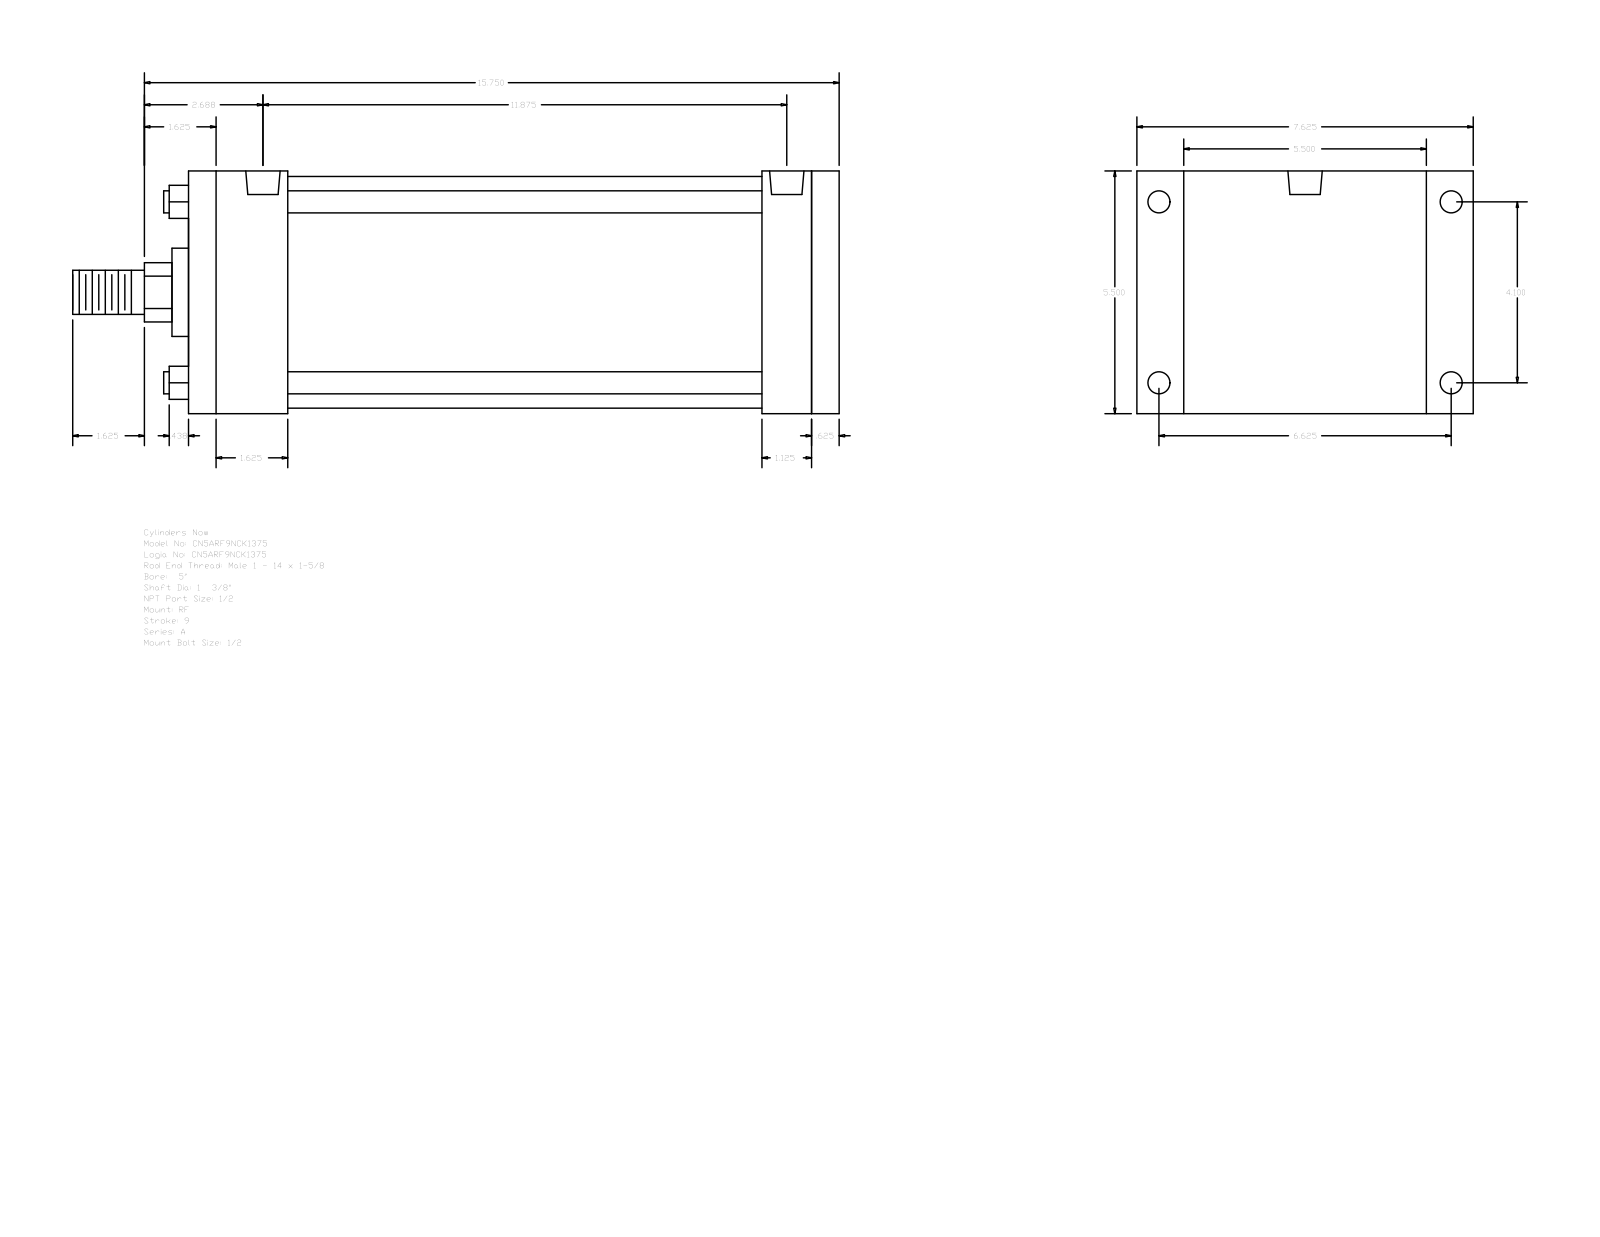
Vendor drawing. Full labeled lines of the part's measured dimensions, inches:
Part name (STEP PRODUCT): A_RF__0500_1.375
STEP written by: GSSL Pune (CONFIG_CONTROL_DESIGN)
Units: inches
Bodies: 0 solids, 92 faces (64 planar, 28 cylindrical, 0 other)
Overall size (bounding box): 17.375 × 7.625 × 5.5
Round holes (diameter × count): ⌀0.344 ×4, ⌀0.5 ×4, ⌀0.778 ×2
Round bosses / shafts (diameter × count): ⌀0.5 ×4, ⌀5.25 ×1, ⌀2 ×1, ⌀1.375 ×1, ⌀1 ×1
Partial cylindrical surfaces — rounded edges, fillets, slot ends (radius × count): R0.672 ×1
Main face-to-face distances: 5.5, 14.75, 14.125, 0.625, 2.25, 1.125, 11.875, 12.5, 13, 10.75
Hole centre spacings: 0.094, 4.1, 6.625, 7.791, 11.687, 11.781, 11.875
